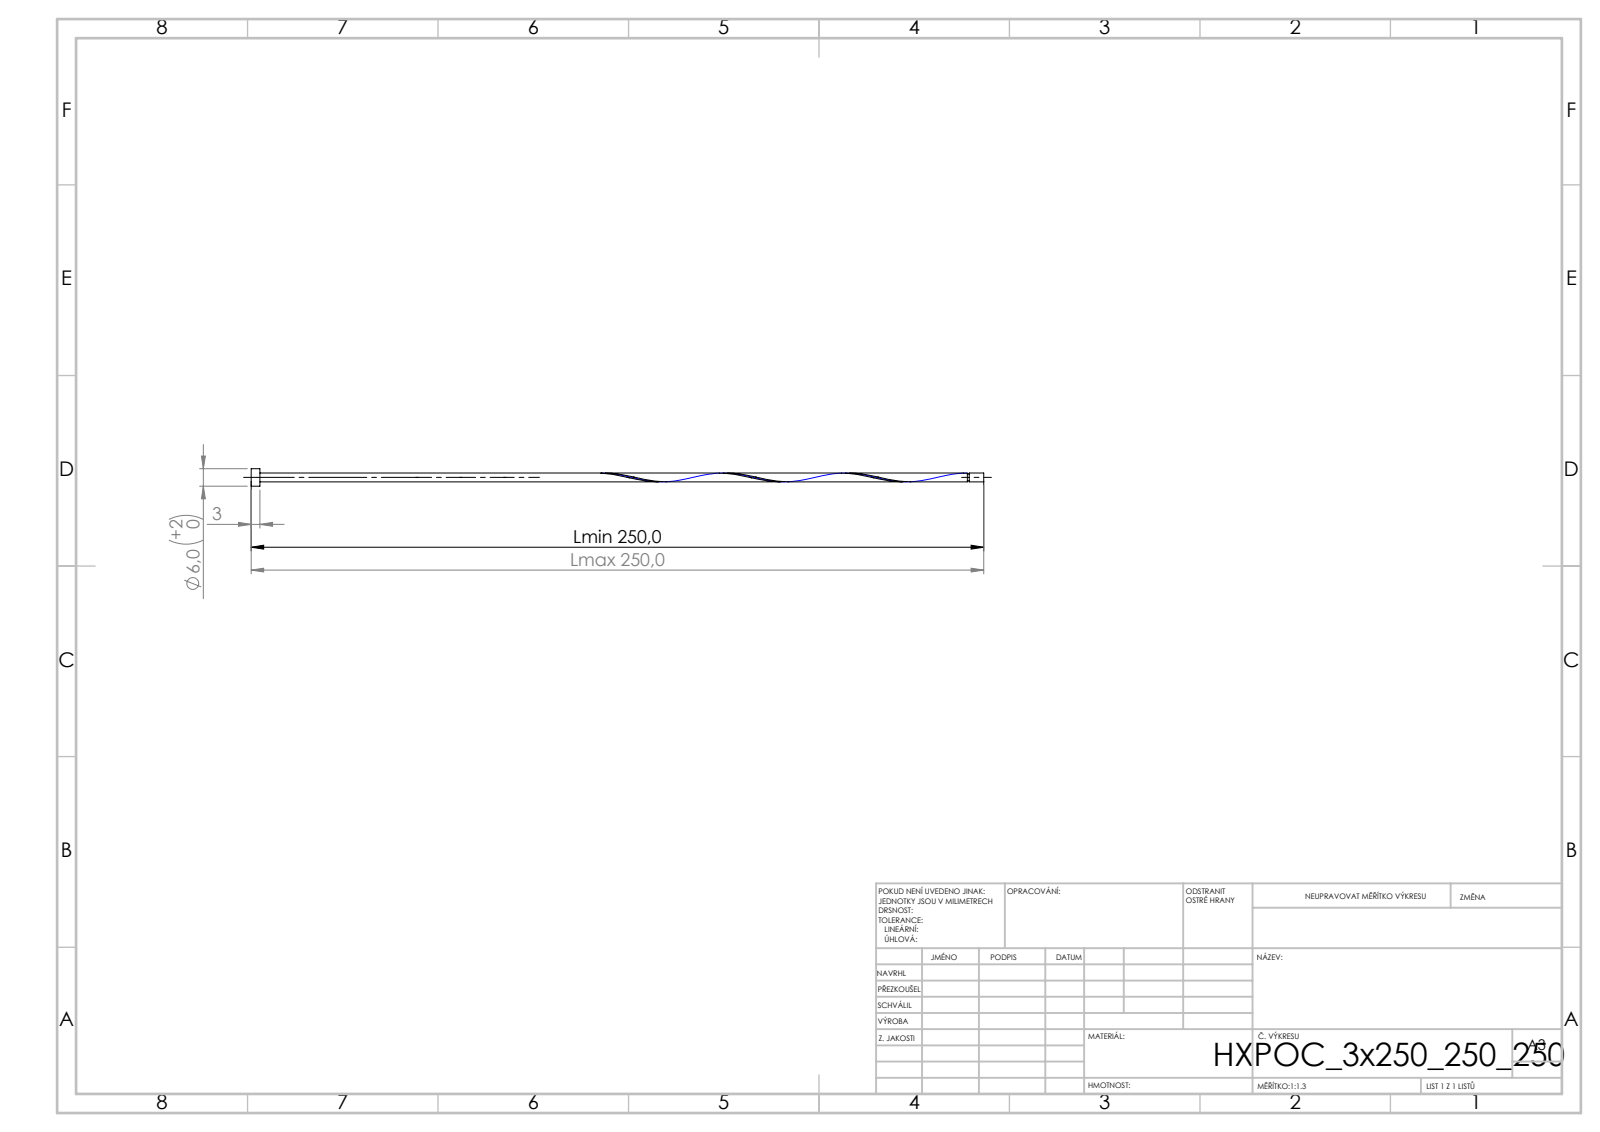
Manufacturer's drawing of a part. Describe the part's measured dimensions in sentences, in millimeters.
Its 3-D file was written by "SolidWorks 2019 (CONFIG_CONTROL_DESIGN)". It is 1 solid with 16 faces: 6 planar, 9 cylindrical and 1 other. Overall it measures 250 by 6 by 6 millimeters. Its volume is 2 205 cubic millimeters and its surface area 3 268 square millimeters. Round bosses or shafts: 1 of diameter 6, 1 of diameter 3, 1 of diameter 2.4. The main face-to-face distances are 3, 250, 247, 245.03, 242.03, 4.97, 244.43, 241.43, 0.6, 5.57.
